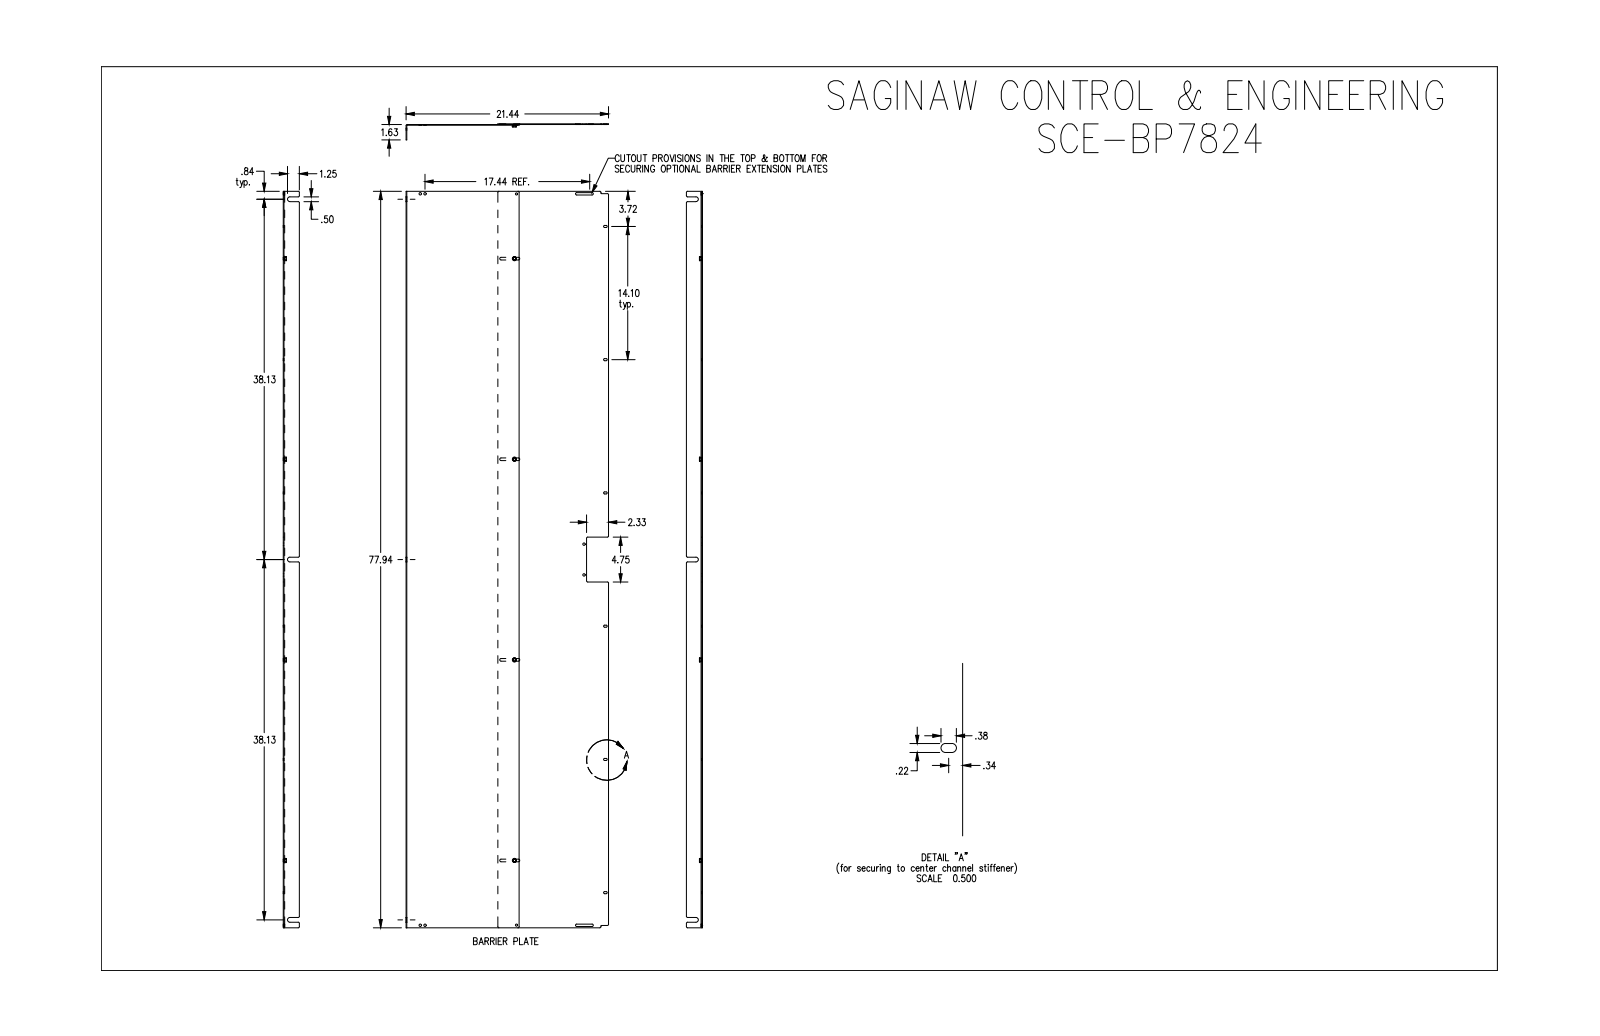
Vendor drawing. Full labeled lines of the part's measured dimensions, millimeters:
Part name (STEP PRODUCT): SCE-BP7824
STEP written by: SolidWorks 2019 (CONFIG_CONTROL_DESIGN)
Units: millimetres
Bodies: 6 solids, 154 faces (67 planar, 75 cylindrical, 12 other)
Overall size (bounding box): 1979.6 × 544.6 × 43.2
Volume: 2 394 000 mm³ · Surface area: 2 534 000 mm²
Round holes (diameter × count): ⌀6.4 ×10, ⌀8.7 ×4, ⌀5.5 ×2
Round bosses / shafts (diameter × count): ⌀11.2 ×4, ⌀8.7 ×4
Partial cylindrical surfaces — rounded edges, fillets, slot ends (radius × count): R3.2 ×24, R2.8 ×12, R3.6 ×8, R6.4 ×3, R1.6 ×2, R1.1 ×1, R3 ×1
Main face-to-face distances: 1.9, 3.8, 246.9, 245, 304, 302.1, 57.2, 43.2, 41.3, 39.4
Hole centre spacings: 539.2, 12.7, 173.9, 246.1, 258.8, 295.2, 297, 307.3
